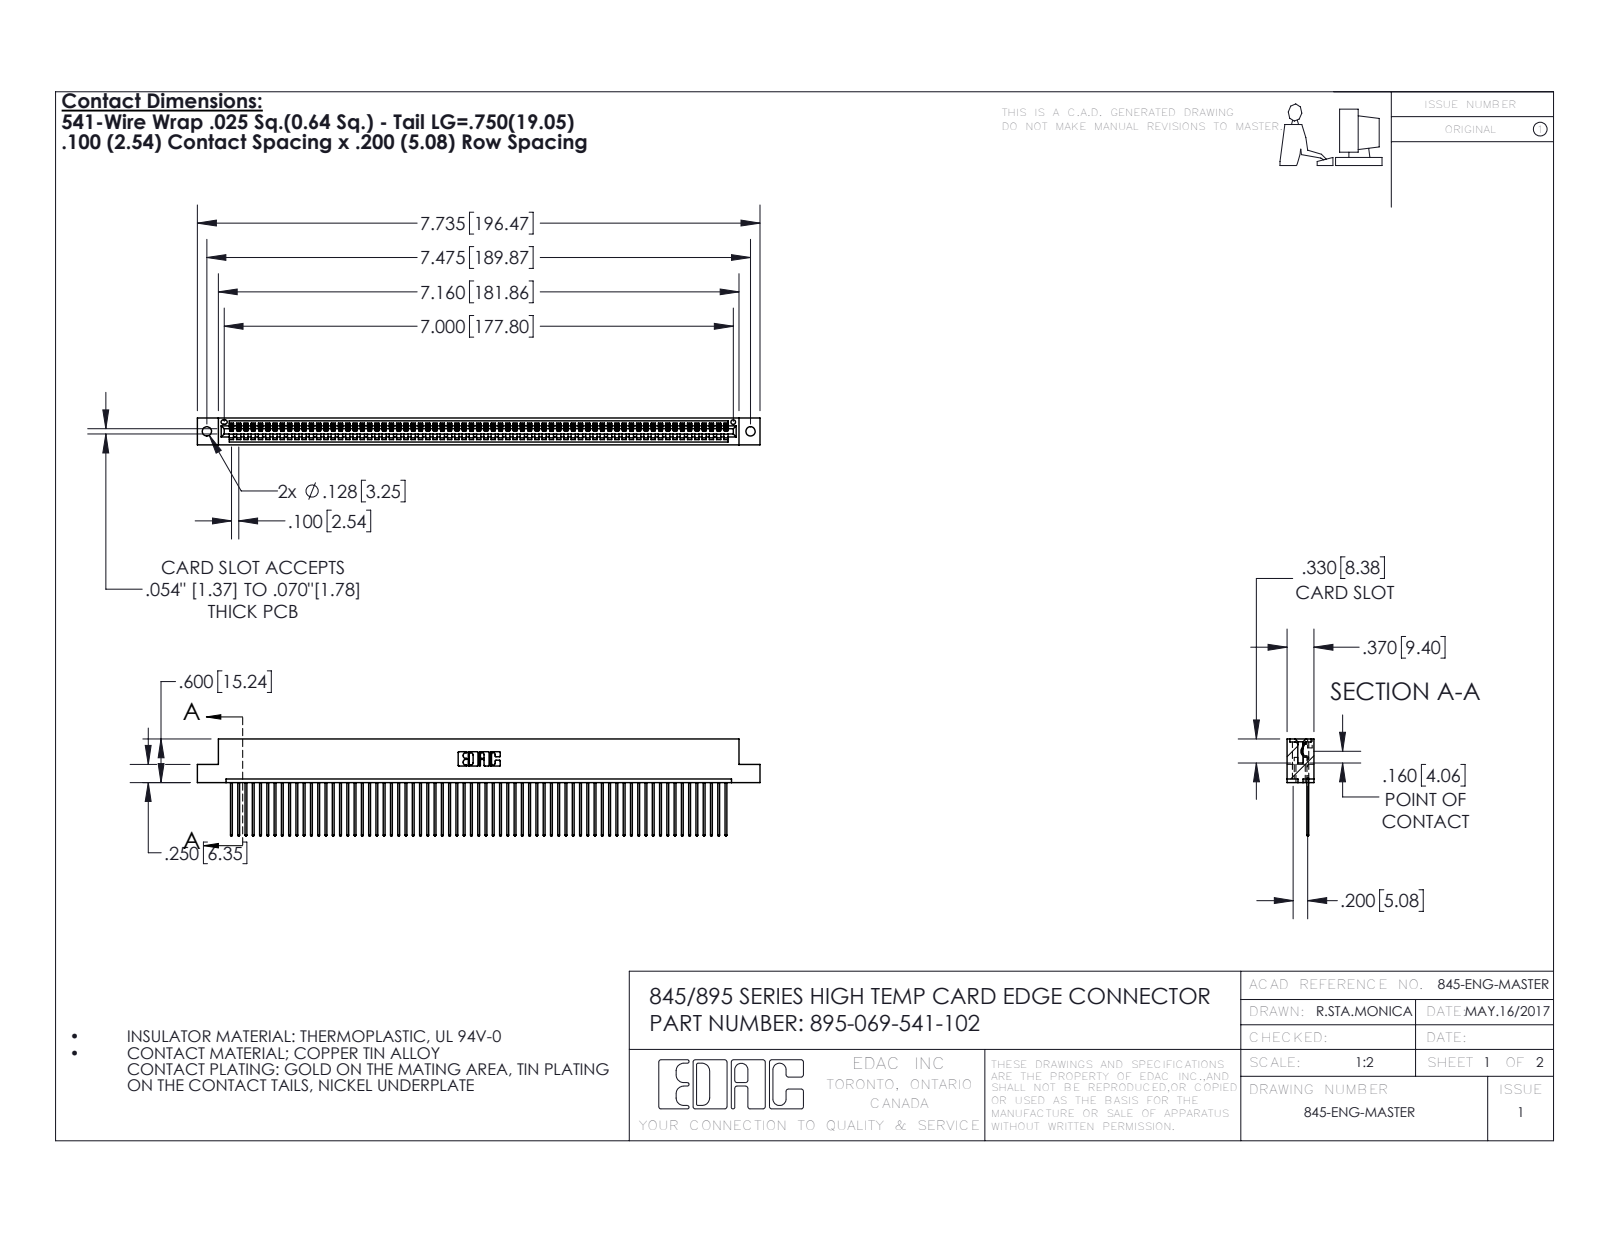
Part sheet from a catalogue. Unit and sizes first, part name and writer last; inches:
Units: inches
Overall size (bounding box): 7.735 × 1.337 × 0.37
Round holes (diameter × count): ⌀0.128 ×2, ⌀0.064 ×1
Partial cylindrical surfaces — rounded edges, fillets, slot ends (radius × count): R0.006 ×138, R0.01 ×138, R0.01 ×22, R0.007 ×6, R0.031 ×6, R0.026 ×3, R0.031 ×2, R0.04 ×2
Main face-to-face distances: 0.072, 0.298, 0.098, 0.272, 0.025, 0.37, 0.2, 0.225, 0.149, 0.072
Hole centre spacings: 0.27, 7.239, 7.475
Volume: 1.164 in³ · Surface area: 41.51 in²
Bodies: 70 solids, 4128 faces (2840 planar, 1288 cylindrical, 0 other)
Part name (STEP PRODUCT): 345 Part_Flush Mounting Lugs - 0.128 Dia; 345-292-001_345-293-141; 395-069-541-102
STEP written by: SolidWorks 2016 (CONFIG_CONTROL_DESIGN)
